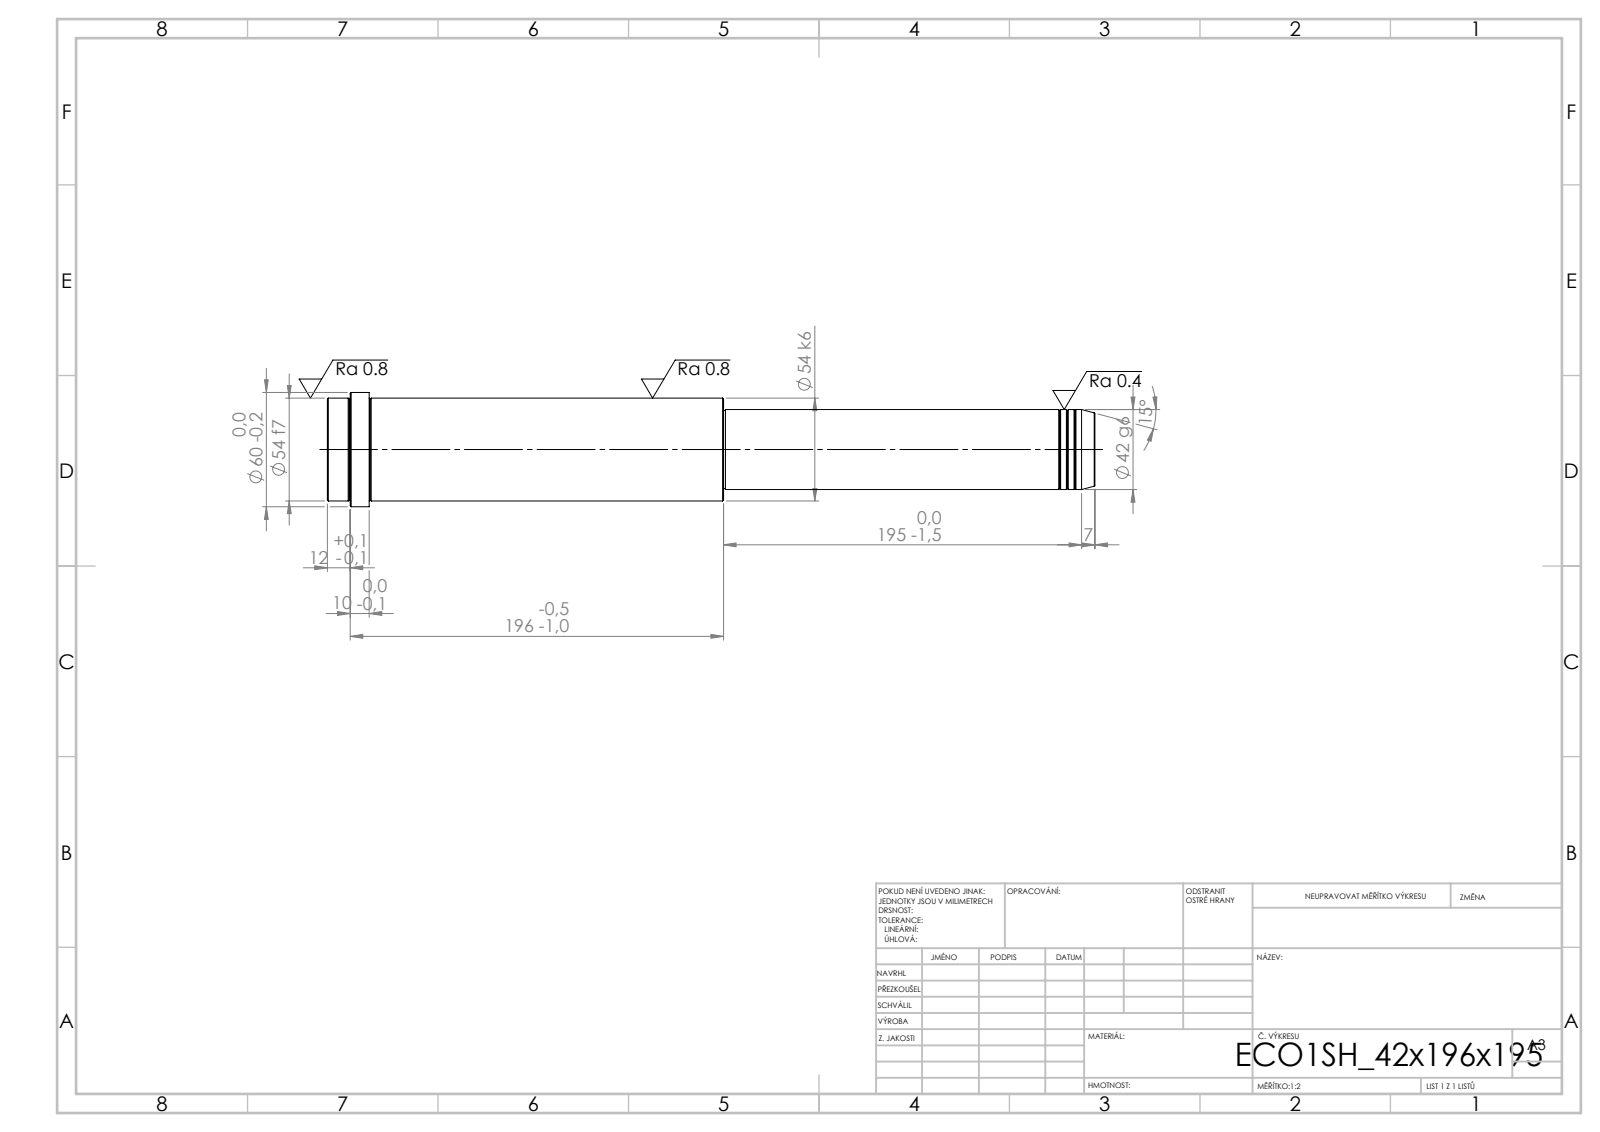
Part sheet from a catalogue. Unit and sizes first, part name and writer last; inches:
Units: inches
Overall size (bounding box): 15.866 × 2.362 × 2.362
Round bosses / shafts (diameter × count): ⌀2.362 ×1, ⌀2.126 ×1, ⌀1.654 ×1, ⌀1.614 ×1
Main face-to-face distances: 15.866, 7.677, 8.189, 15, 7.323, 0.866, 15.394, 7.717, 0.394, 0.472
Volume: 45.81 in³ · Surface area: 103.8 in²
Bodies: 1 solid, 52 faces (6 planar, 16 cylindrical, 30 other)
STEP written by: SolidWorks 2019 (CONFIG_CONTROL_DESIGN)
